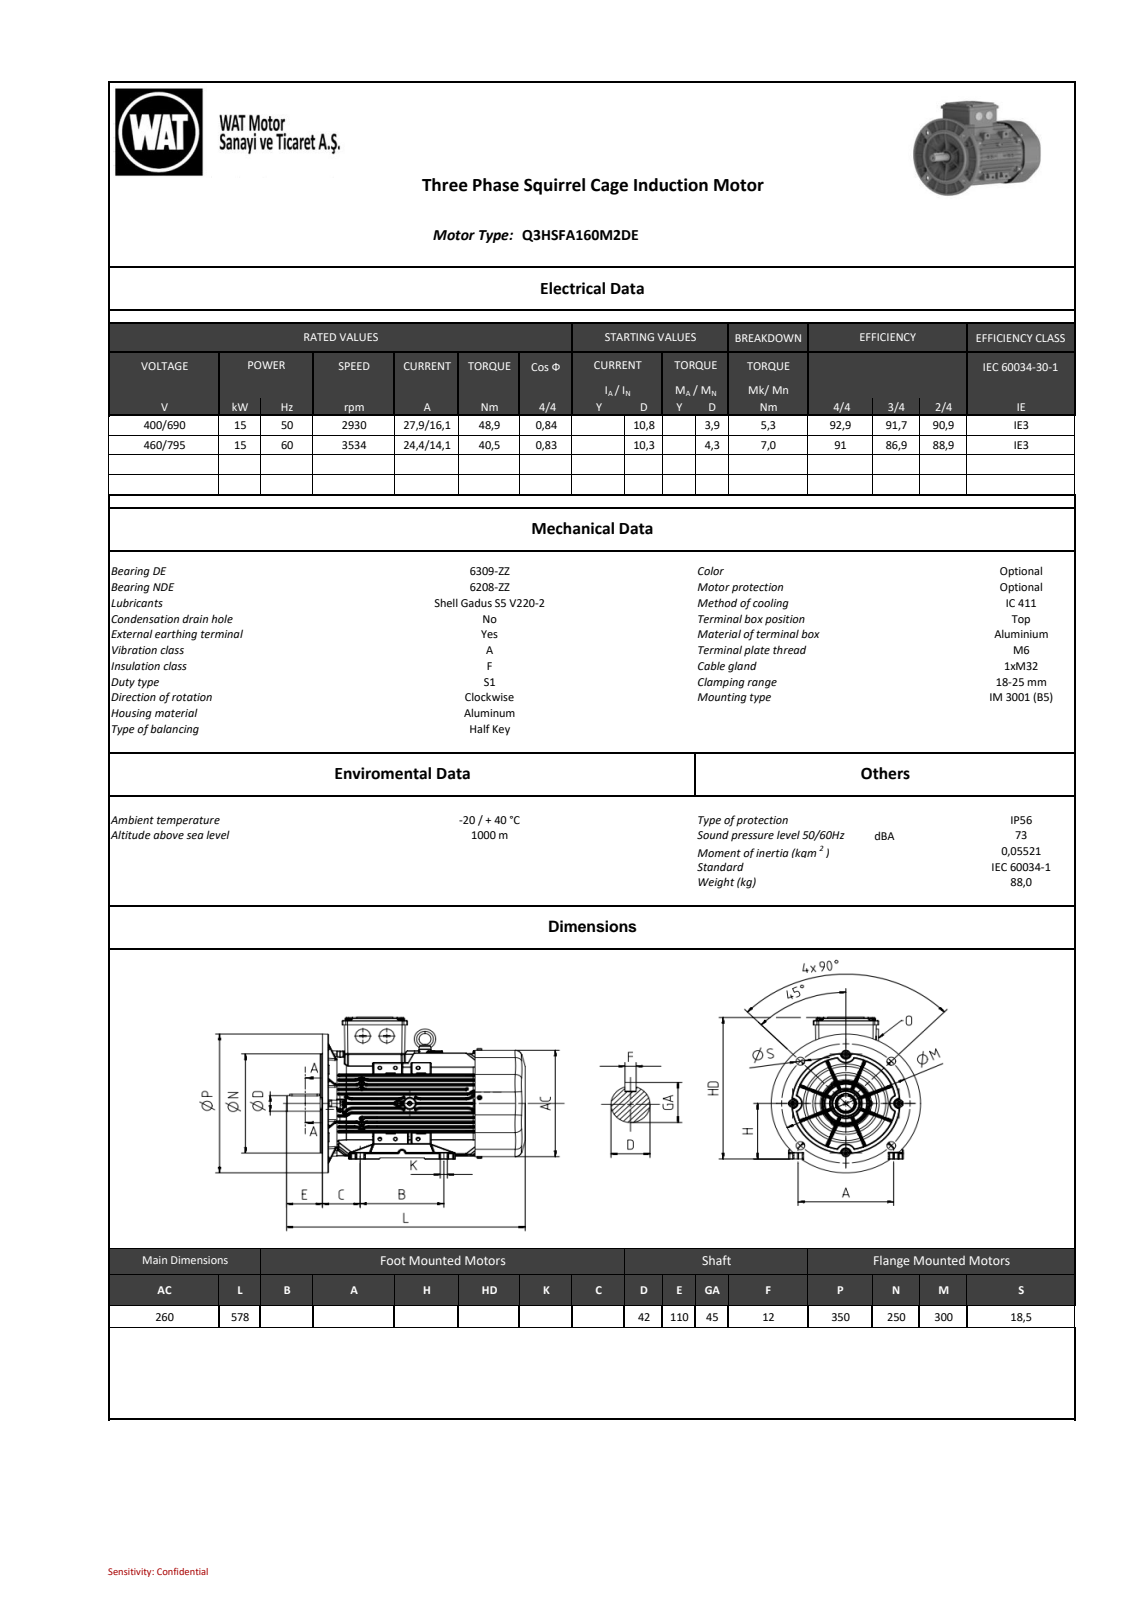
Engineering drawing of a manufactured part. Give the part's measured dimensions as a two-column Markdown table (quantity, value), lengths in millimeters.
| quantity | value |
| --- | --- |
| part name | QHS series_ 160_B5 _DEEP COVER__stp_objects |
| STEP written by | SIEMENS PLM Software NX2206.8101 (AP203_CONFIGURATION_CONTROLLED_3D_DESIGN_OF_MECHANICAL_PARTS_AND_ASSEMBLIES_MIM_LF) |
| units | millimeters |
| bodies | 0 solids, 6789 faces (1758 planar, 3019 cylindrical, 2012 other) |
| overall size | 578 × 365.15 × 349.89 |
| round holes (diameter × count) | 17 × 5, 4.6 × 3, 8.47 × 2, 8.03 × 1, 8.48 × 1, 8.48 × 1, 8.57 × 1, 8.61 × 1, 16 × 1, 68.67 × 1, 82 × 1, 180 × 1 |
| round bosses / shafts (diameter × count) | 13 × 4, 8 × 4, 38 × 2, 250 × 1, 230.5 × 1, 86.77 × 1, 45 × 1, 42 × 1 |
| partial cylindrical surfaces (radius × count) | 0.8 × 962, 1 × 811, 3 × 79, 2 × 66, 1.5 × 58, 7 × 48, 5 × 17, 0.5 × 16 |
| main face-to-face distances | 1.5, 10.42, 10.56, 10.28, 7, 14, 20.84, 125.58, 115.18, 104.9 |
| hole center spacings | 120.5, 170.41, 125, 178.91, 241, 31.88, 89.32, 89.62 |
